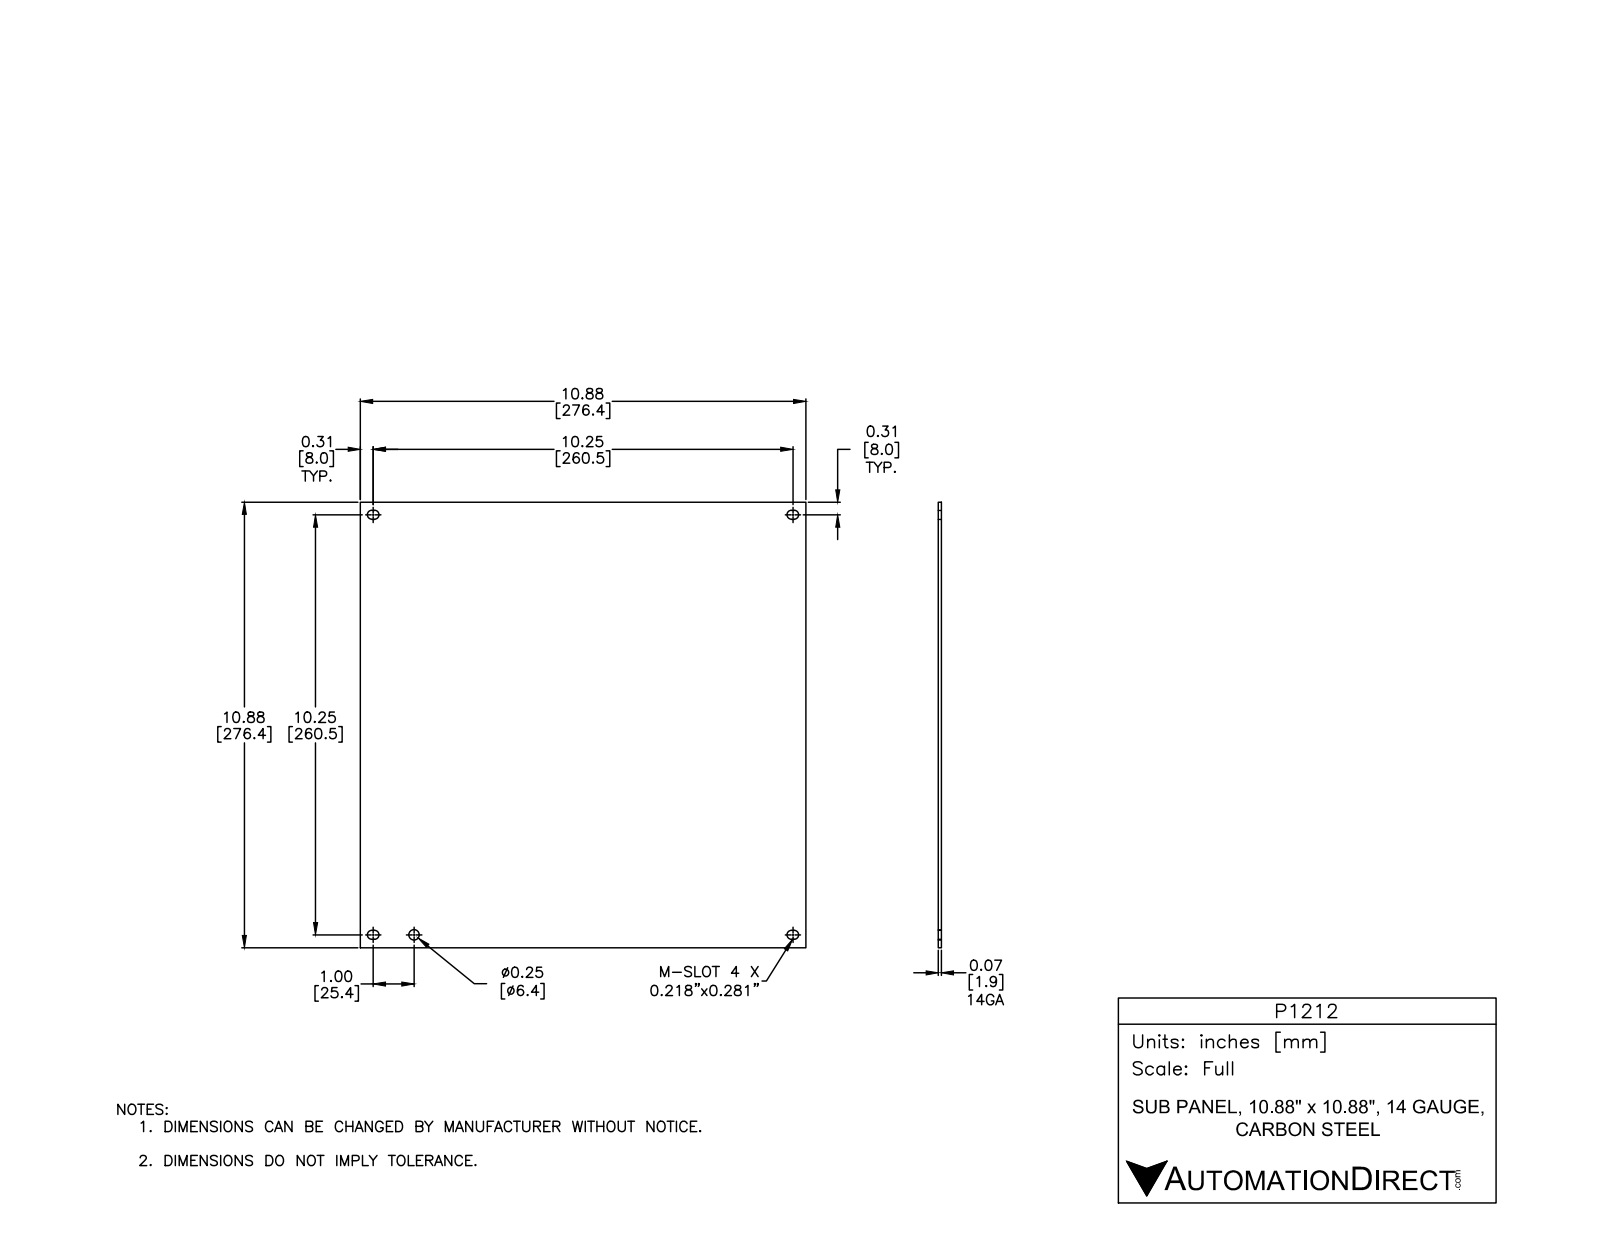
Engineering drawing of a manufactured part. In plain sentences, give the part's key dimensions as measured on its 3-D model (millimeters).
The part is named "P1212". Its 3-D file was written by "Autodesk Inventor 2012 (AUTOMOTIVE_DESIGN)". It is 1 solid with 23 faces: 14 planar, 9 cylindrical and 0 other. Overall it measures 276.4 by 276.4 by 1.9 millimeters. Its volume is 143 200 cubic millimeters and its surface area 154 700 square millimeters. Round holes: 1 of diameter 6.4. Partial cylindrical surfaces (rounded edges, fillets, slot ends): 8 of radius 2.8. The main face-to-face distances are 1.9, 276.4, 5.2, 10.7, 265.6, 271.2, 5.5, 260.5, 266, 254.9.
